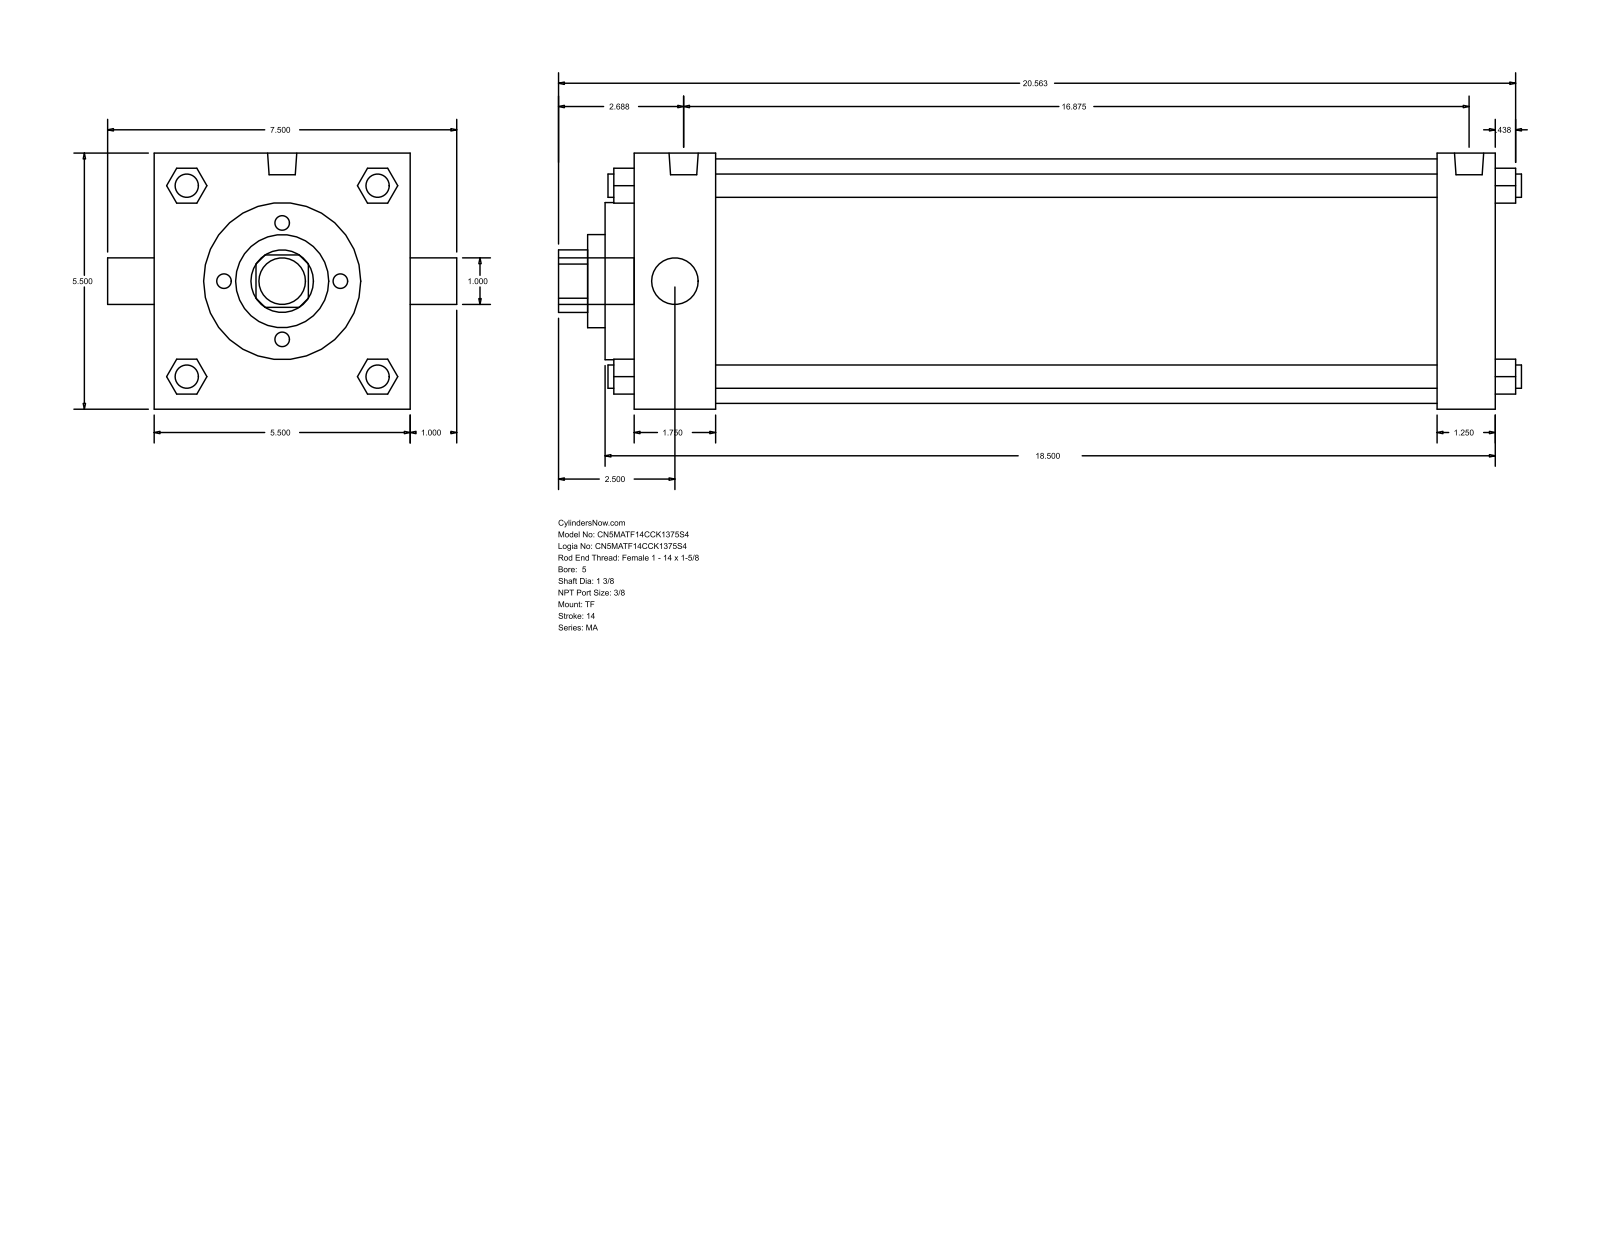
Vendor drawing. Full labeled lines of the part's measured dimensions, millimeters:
Part name (STEP PRODUCT): MA_TF__0500_1.375
STEP written by: GSSL Pune (CONFIG_CONTROL_DESIGN)
Units: millimetres
Bodies: 0 solids, 122 faces (93 planar, 29 cylindrical, 0 other)
Overall size (bounding box): 525.46 × 190.5 × 139.7
Round holes (diameter × count): ⌀25.4 ×1, ⌀34.92 ×1, ⌀50.8 ×1, ⌀85.72 ×1, ⌀133.35 ×1
Round bosses / shafts (diameter × count): ⌀12.7 ×4, ⌀11.11 ×3, ⌀15.93 ×2, ⌀25.4 ×1
Partial cylindrical surfaces — rounded edges, fillets, slot ends (radius × count): R17.06 ×1
Main face-to-face distances: 139.7, 469.91, 438.16, 31.75, 44.45, 393.71, 425.46, 15.87, 60.32, 454.03
